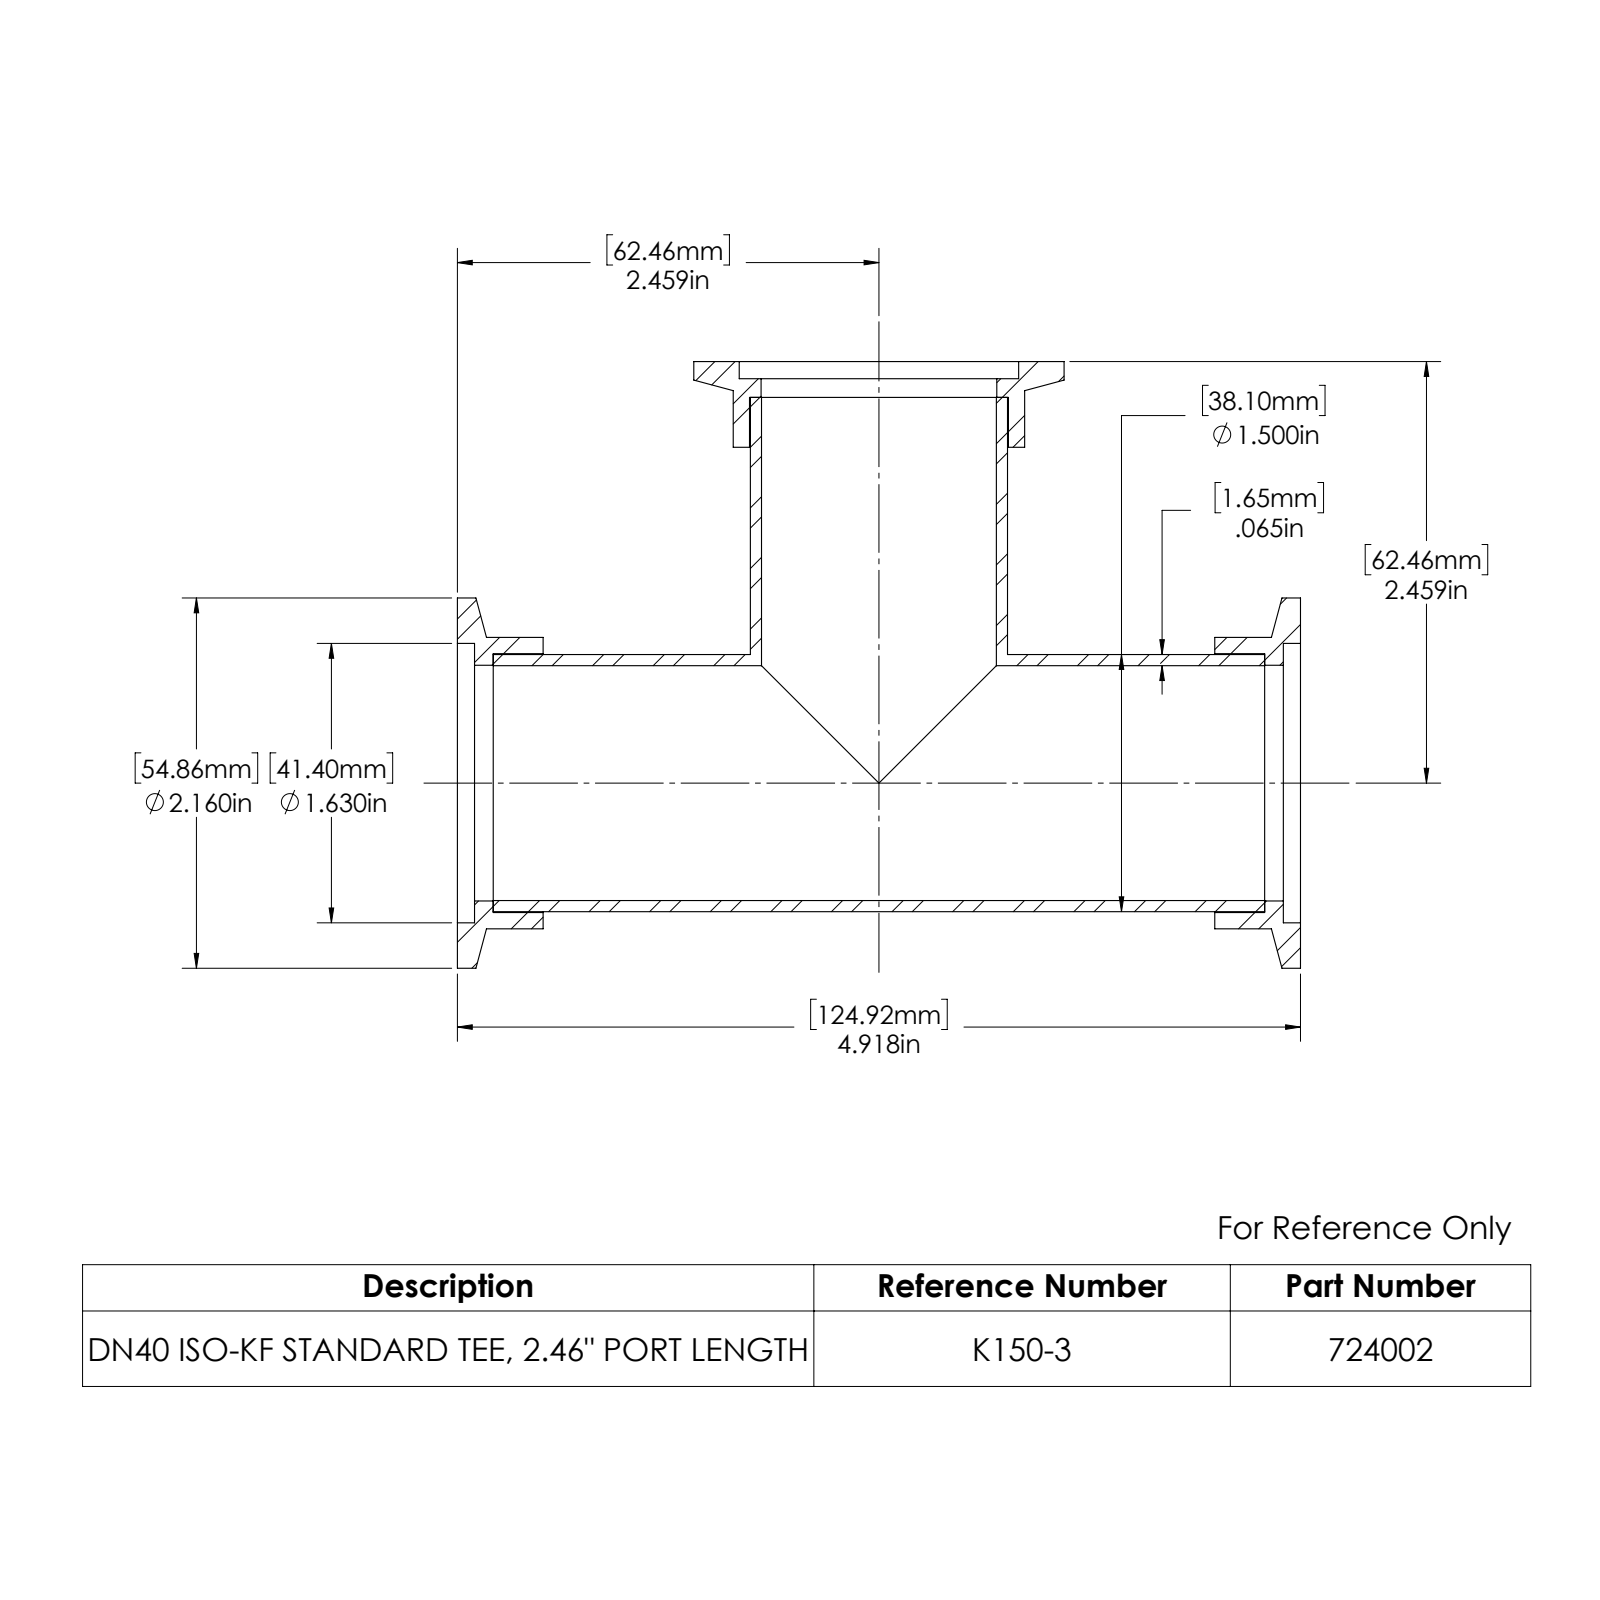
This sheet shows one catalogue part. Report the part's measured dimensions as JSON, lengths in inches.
{"part_name": "713003-99; 404502; 724002", "step_written_by": "SolidWorks 2022 (AUTOMOTIVE_DESIGN)", "units": "inches", "bodies": {"solids": 4, "faces": 59, "planar": 15, "cylindrical": 38, "other": 6}, "overall_size": [4.918, 3.539, 2.16], "volume_in3": 3.015, "surface_area_in2": 81.29, "round_holes": [[1.37, 2], [1.375, 2], [1.51, 2], [1.63, 2]], "round_bosses_or_shafts": [[2.16, 2], [1.7, 2], [1.5, 2]], "face_to_face_distances": [0.1, 0.209, 0.109, 4.918, 0.5, 0.4, 0.291, 4.818, 4.709, 4.609]}
